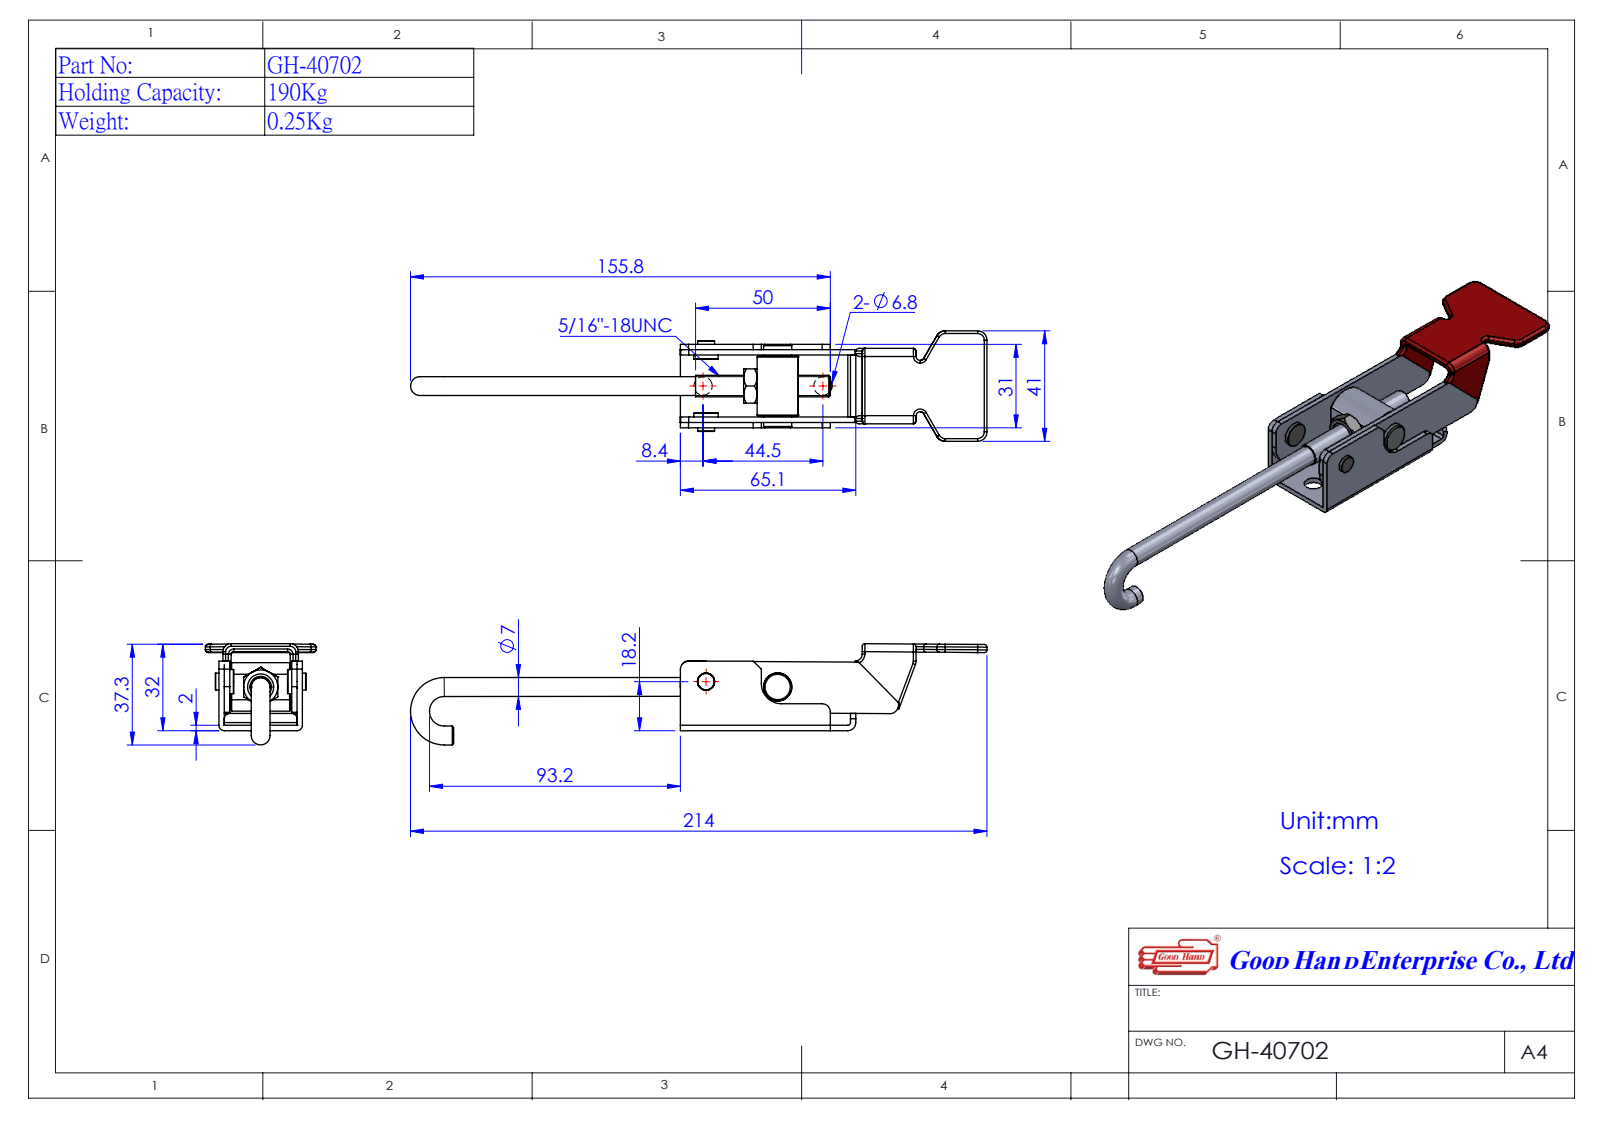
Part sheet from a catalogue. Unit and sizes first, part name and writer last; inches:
Units: inches
Overall size (bounding box): 8.425 × 1.614 × 1.48
Round holes (diameter × count): ⌀0.268 ×2, ⌀0.197 ×1, ⌀0.313 ×1, ⌀0.315 ×1
Round bosses / shafts (diameter × count): ⌀0.276 ×2, ⌀0.354 ×1, ⌀0.313 ×1
Partial cylindrical surfaces — rounded edges, fillets, slot ends (radius × count): R0.039 ×25, R0.118 ×8, R0.138 ×5, R0.059 ×2, R0.079 ×2, R0.079 ×2, R0.098 ×1, R0.295 ×1
Main face-to-face distances: 0.079, 1.063, 0.984, 0.157, 1.142, 0.118, 0.906, 1.22, 0.098, 0.02
Hole centre spacings: 1.05, 1.752
Volume: 1.938 in³ · Surface area: 39.93 in²
Bodies: 6 solids, 268 faces (101 planar, 99 cylindrical, 68 other)
Part name (STEP PRODUCT): Group3^GH-40702(簡化); 14070213-1^GH-40702(簡化); 44070265-1^GH-40702(簡化); GH-40702(簡化) (+1 more)
STEP written by: SolidWorks 2016 (AUTOMOTIVE_DESIGN)
